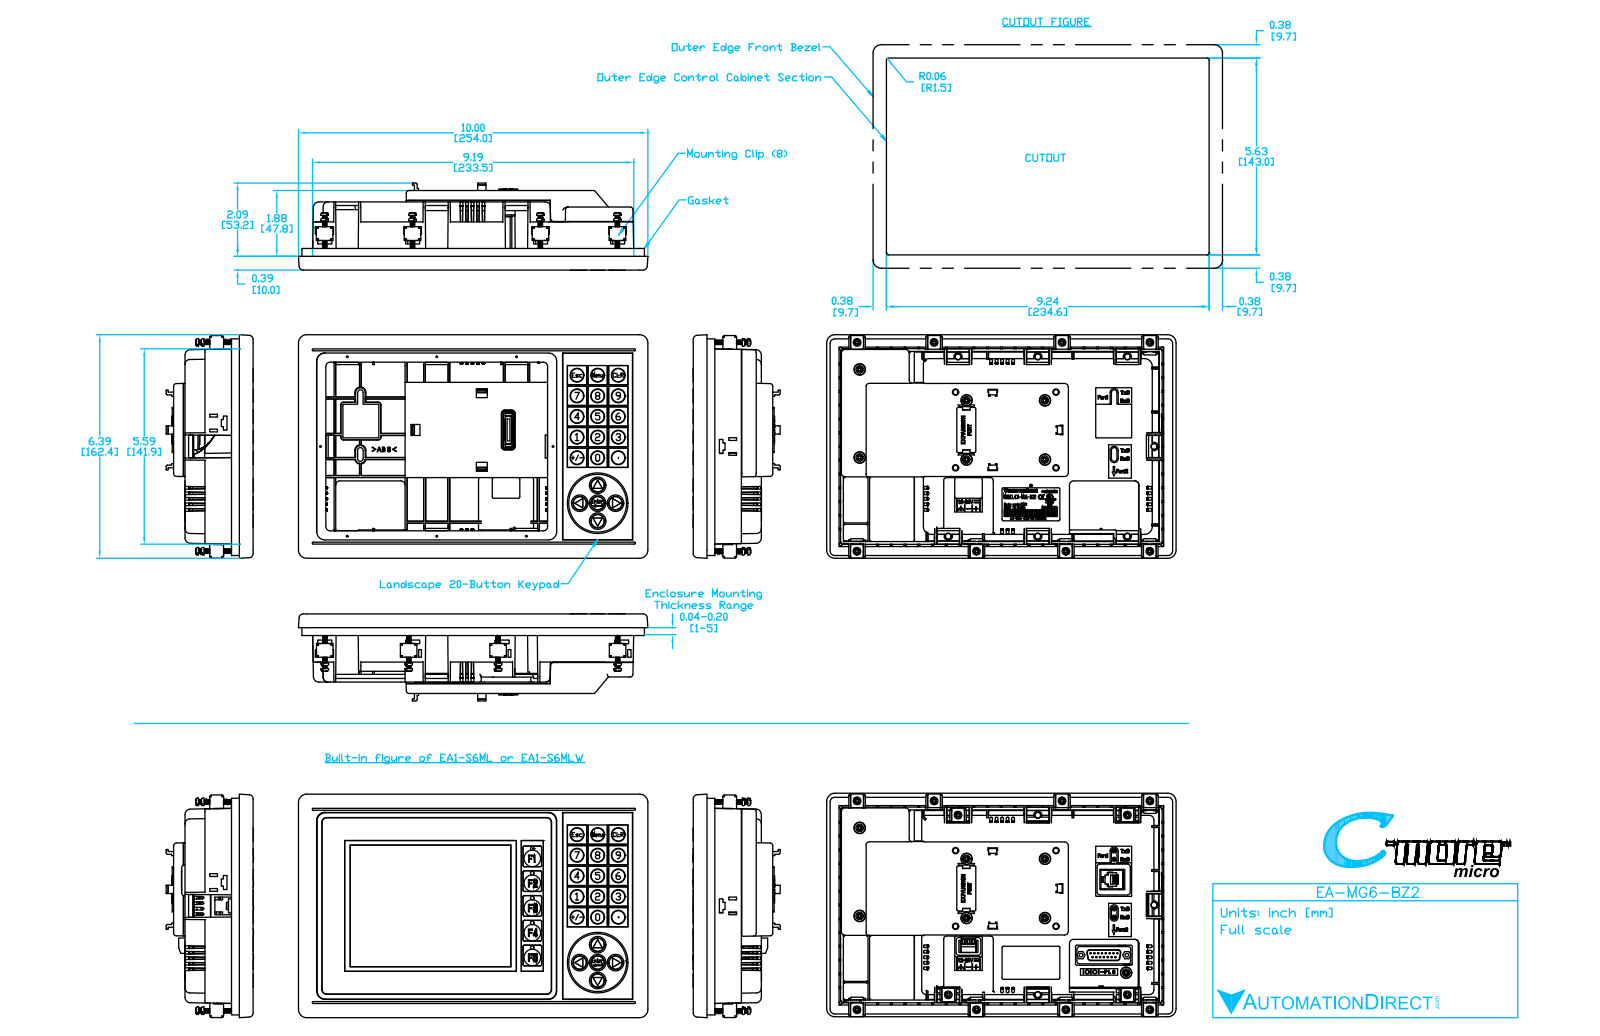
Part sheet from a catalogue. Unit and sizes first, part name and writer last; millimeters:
Units: millimetres
Overall size (bounding box): 174 × 135.4 × 52.4
Round holes (diameter × count): ⌀2.3 ×5, ⌀11 ×5, ⌀8 ×4, ⌀6.88 ×1
Round bosses / shafts (diameter × count): ⌀5.3 ×5
Partial cylindrical surfaces — rounded edges, fillets, slot ends (radius × count): R1 ×34, R2 ×16, R2.5 ×8, R0.5 ×4, R3.98 ×4, R4 ×4, R6 ×4
Main face-to-face distances: 3, 39.9, 9, 12, 42.9, 118.3, 109.3, 106.3, 156.9, 147.9
Hole centre spacings: 18.2, 36.4, 7, 11.2, 25.2, 54.6, 29.4, 43.4
Volume: 706 908 mm³ · Surface area: 168 604 mm²
Bodies: 19 solids, 656 faces (465 planar, 163 cylindrical, 28 other)
Part name (STEP PRODUCT): EA1-S6MLW
STEP written by: SolidWorks 2009 (CONFIG_CONTROL_DESIGN)
